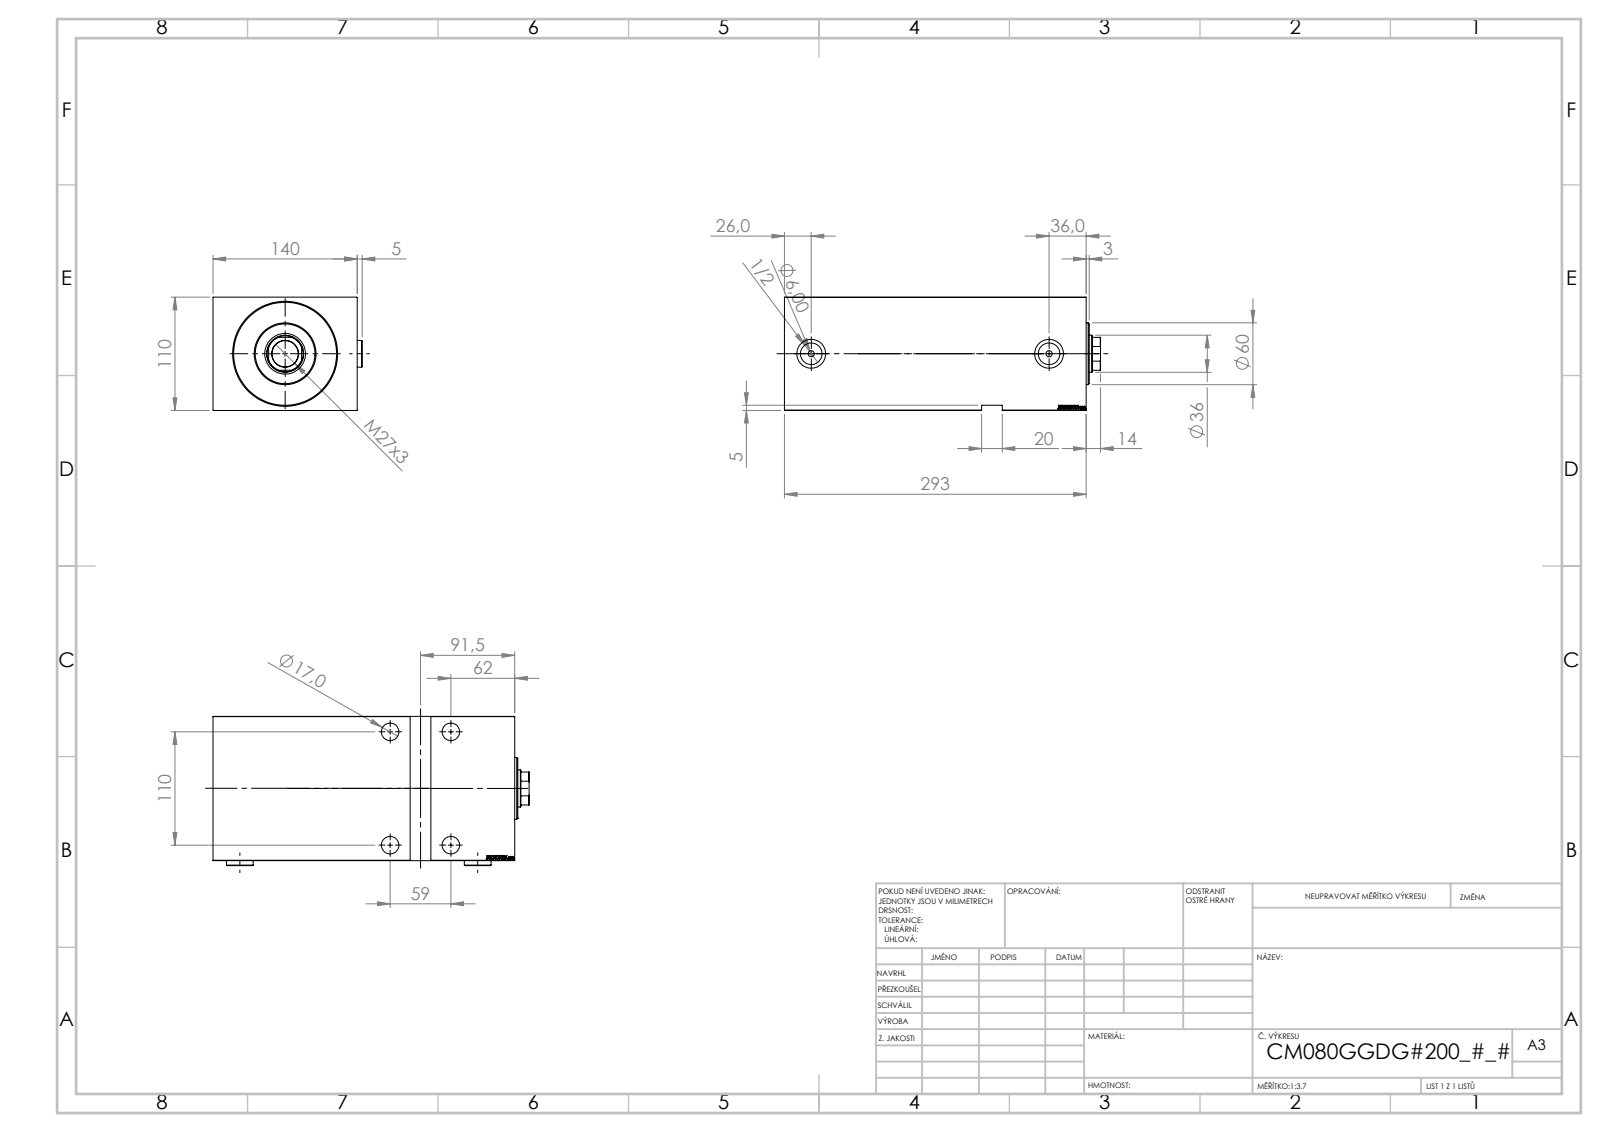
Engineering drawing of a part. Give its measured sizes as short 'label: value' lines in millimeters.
name: V450CM_G_VCP; Zatka_OIL_PORT; V450CM_VC_G; V450CM_G_Body
written by: SolidWorks 2019 (CONFIG_CONTROL_DESIGN)
unit: mm
bodies: 5 solids, 912 faces (446 planar, 68 cylindrical, 398 other)
size: 307 × 144.9 × 110
volume: 3 517 000 mm³; area: 348 207 mm²
holes: 4× ⌀17, 4× ⌀25, 2× ⌀6, 2× ⌀20.96, 2× ⌀28, 1× ⌀25.5, 1× ⌀36, 1× ⌀39.5, 1× ⌀80, 1× ⌀82, 1× ⌀100
bosses: 2× ⌀26, 1× ⌀60
rounds: 1× R17.5
face distances: 110, 140, 5, 293, 21, 272, 288, 267, 79, 58
hole spacings: 59, 110, 124.82, 231
